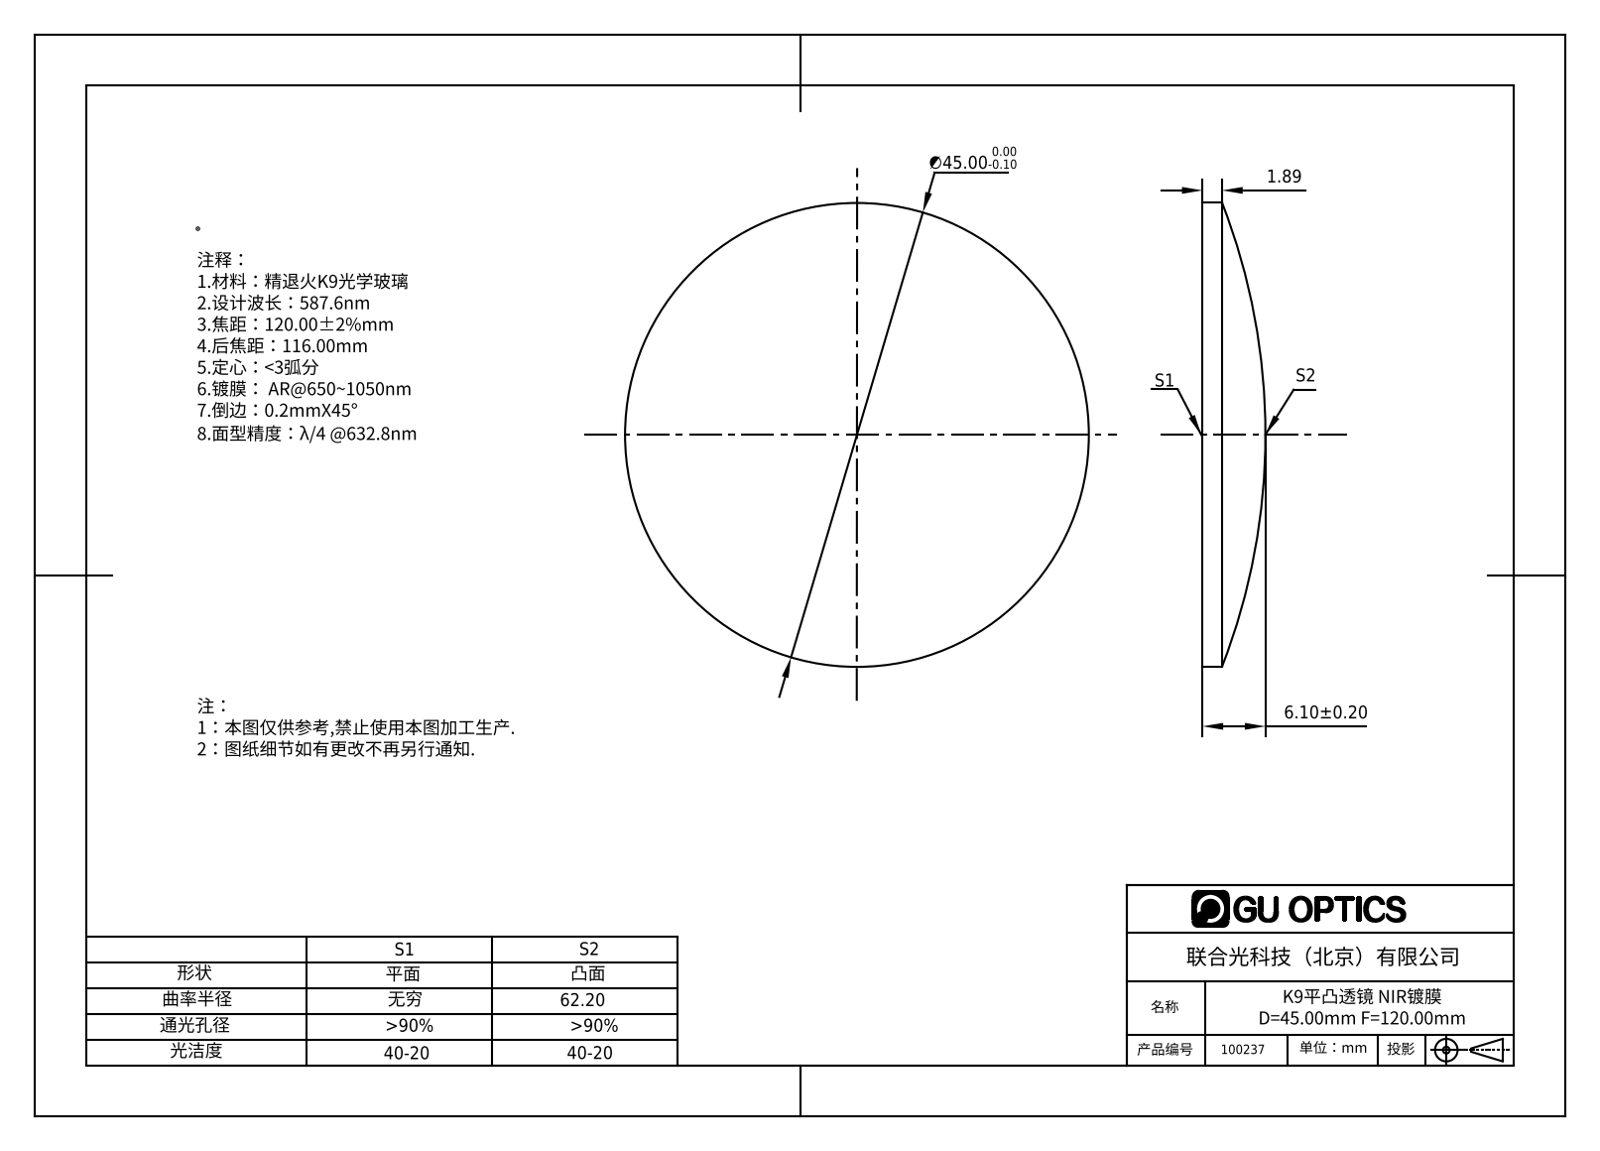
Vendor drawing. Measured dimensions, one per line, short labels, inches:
name: 100237
written by: SolidWorks 2016 (AUTOMOTIVE_DESIGN)
unit: in
bodies: 1 solid, 5 faces (1 planar, 2 cylindrical, 2 other)
size: 1.772 × 1.772 × 0.24
volume: 0.39 in³; area: 5.431 in²
bosses: 1× ⌀1.772
